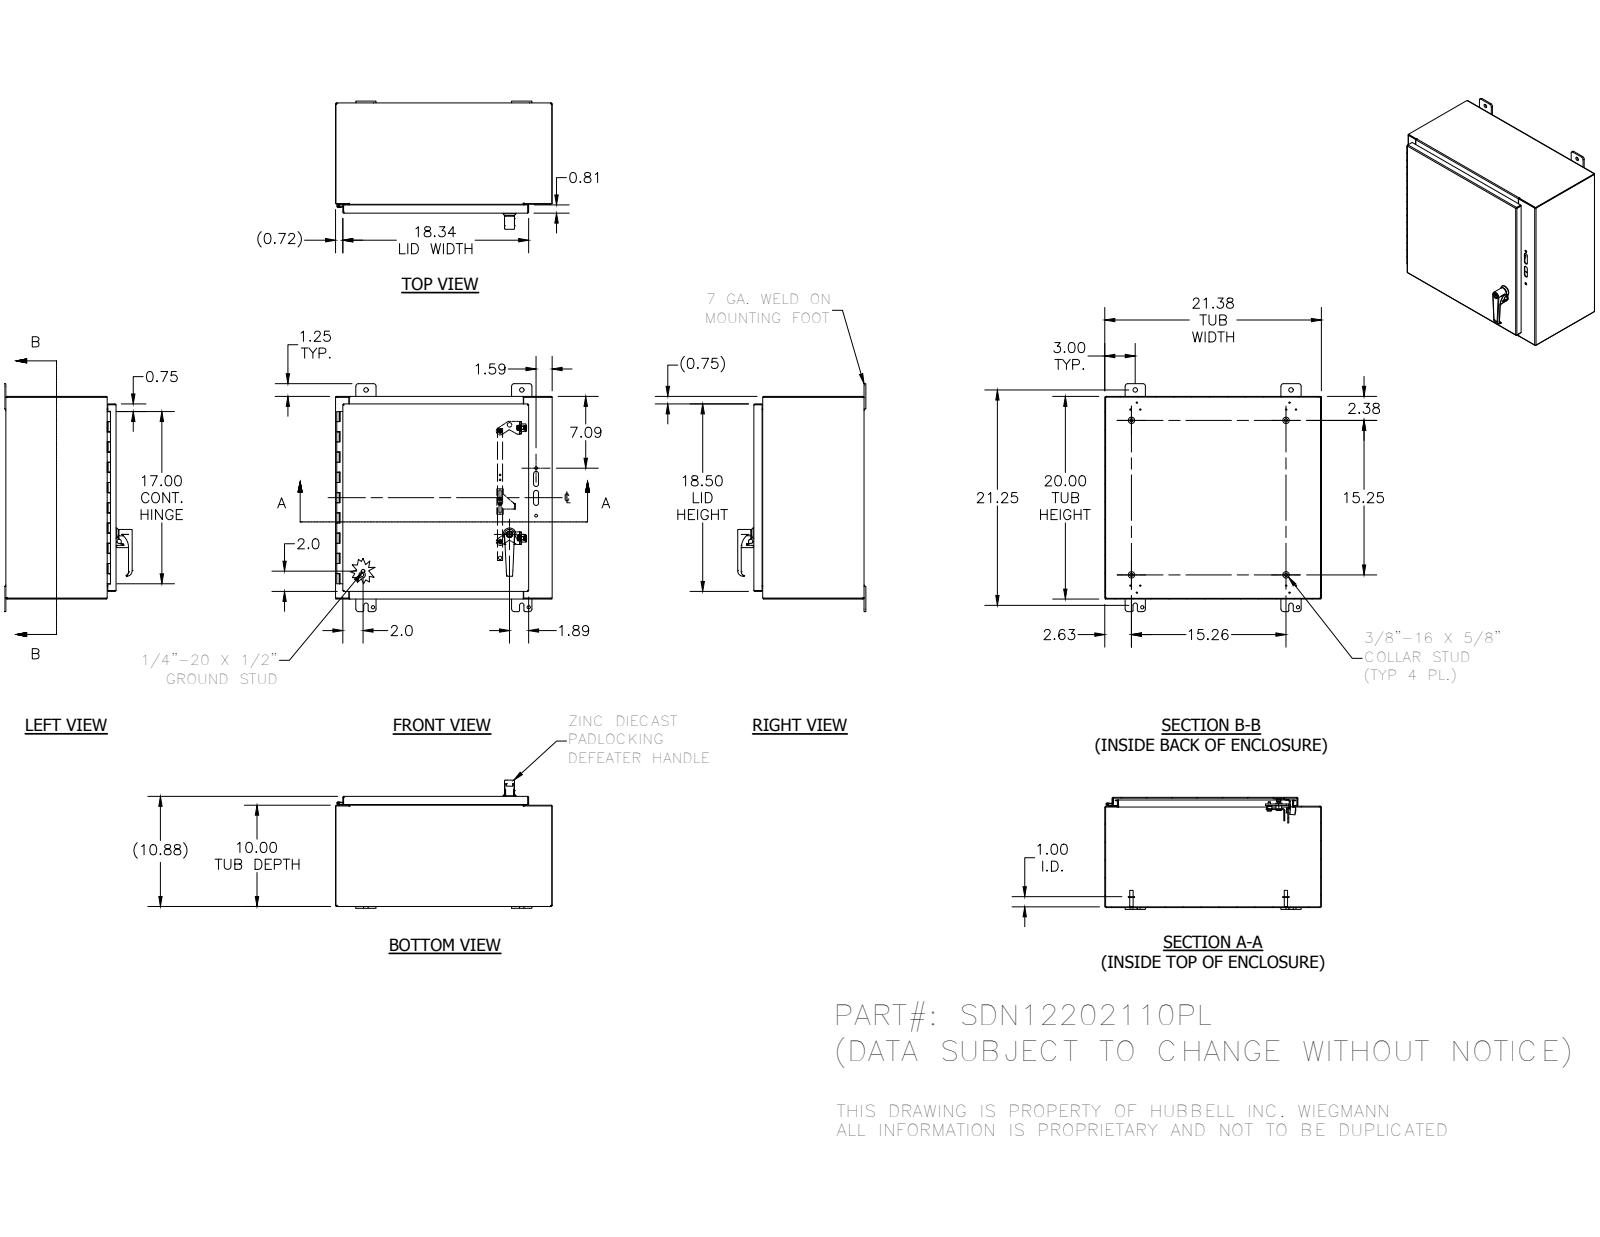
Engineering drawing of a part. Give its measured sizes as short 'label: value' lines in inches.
name: SDN12202110PL
written by: SolidWorks 2019 (AUTOMOTIVE_DESIGN)
unit: in
bodies: 49 solids, 1511 faces (770 planar, 513 cylindrical, 228 other)
size: 22.5 × 21.38 × 12.649
volume: 146.2 in³; area: 3 880 in²
holes: 12× ⌀0.12, 4× ⌀0.145, 4× ⌀0.313, 4× ⌀0.438, 3× ⌀0.32, 2× ⌀0.156, 2× ⌀0.196, 2× ⌀0.211, 2× ⌀0.22, 2× ⌀0.281, 2× ⌀0.313, 2× ⌀0.45
bosses: 5× ⌀0.33, 4× ⌀0.437, 4× ⌀0.3, 4× ⌀0.25, 4× ⌀0.19, 3× ⌀0.625, 2× ⌀0.75, 2× ⌀0.625
rounds: 38× R0.02, 31× R0.012, 22× R0.25, 20× R0.031, 20× R0.105, 17× R0.125, 16× R0.025, 8× R0.07
face distances: 0.074, 10.801, 19.926, 21.306, 10.727, 10.875, 9.926, 0.875, 20, 19.852
hole spacings: 0.759, 1.593, 10.9, 14.752, 15.38, 17.38, 18.069, 18.077
